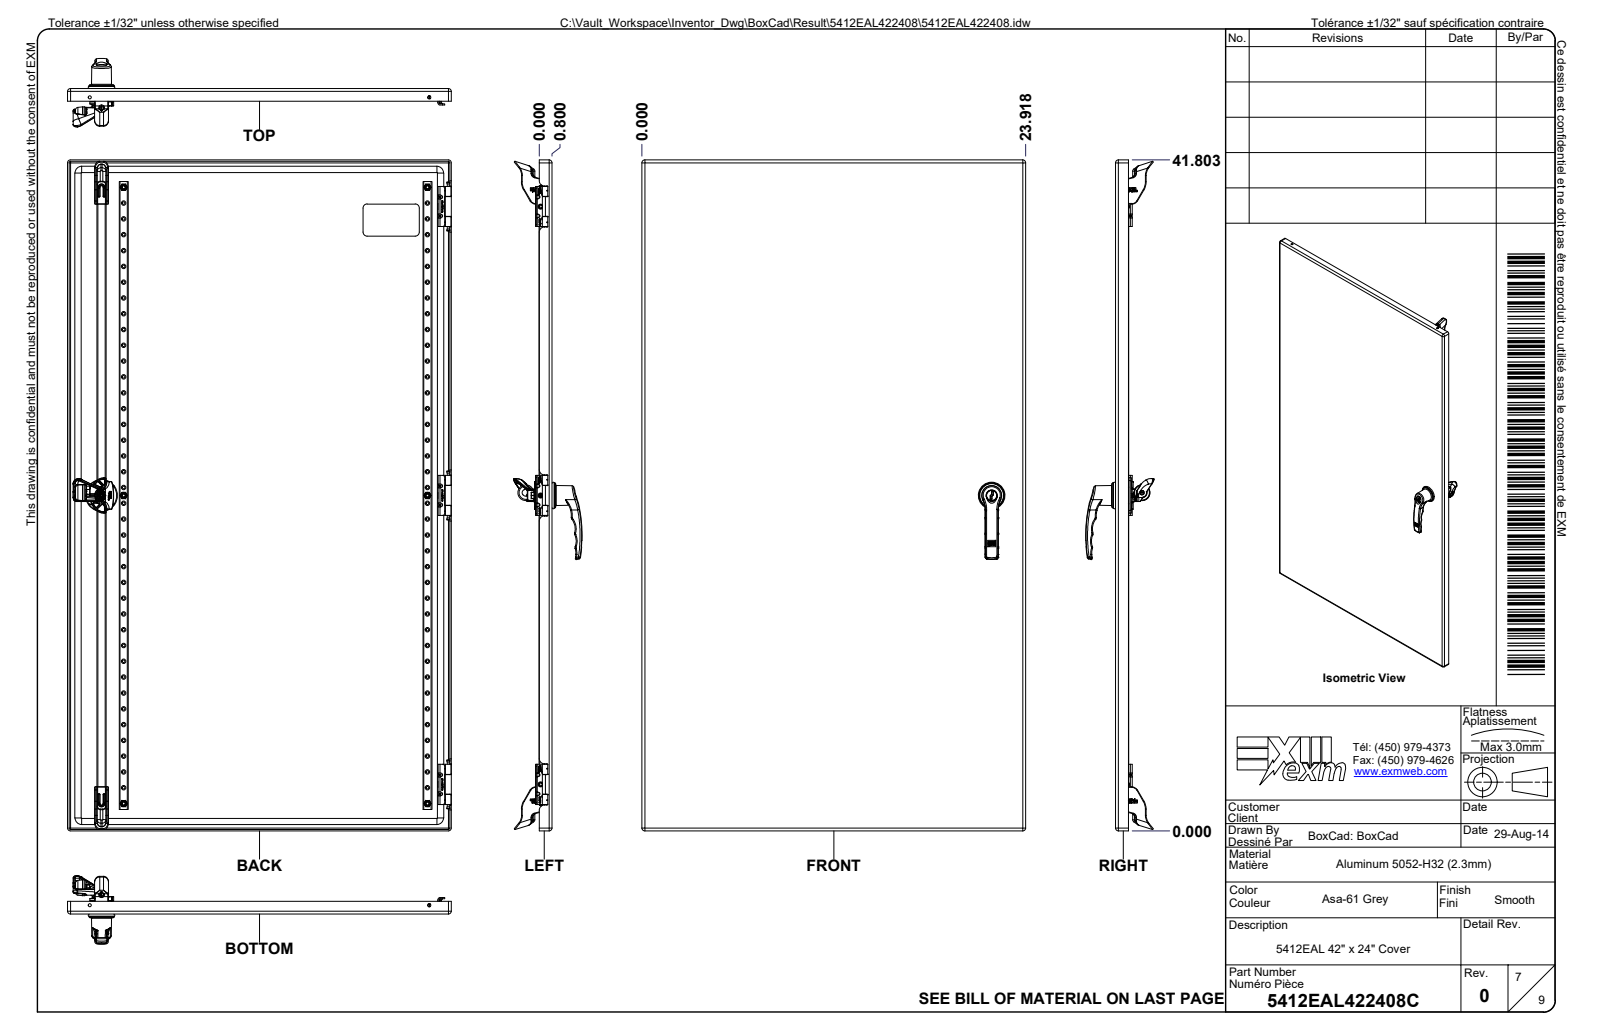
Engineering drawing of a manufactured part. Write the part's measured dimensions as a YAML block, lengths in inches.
part_name: "5412EAL422408; 5412EAL422408B; 5412EAL422408B-P; STK-Q-16010 (+8 more)"
step_written_by: "Autodesk Inventor 2024 (AUTOMOTIVE_DESIGN)"
units: inches
bodies: {solids: 90, faces: 9531, planar: 3634, cylindrical: 2085, other: 3812}
overall_size: [42, 24.042, 10.933]
volume: 427.5
surface_area: 9352
round_holes:
  - {diameter: 0.165, count: 76}
  - {diameter: 0.03, count: 15}
  - {diameter: 0.201, count: 10}
  - {diameter: 0.315, count: 10}
  - {diameter: 0.311, count: 9}
  - {diameter: 0.29, count: 7}
  - {diameter: 0.044, count: 6}
  - {diameter: 0.197, count: 6}
  - {diameter: 0.268, count: 6}
  - {diameter: 0.27, count: 6}
  - {diameter: 0.5, count: 6}
  - {diameter: 0.39, count: 4}
round_bosses_or_shafts:
  - {diameter: 0.237, count: 76}
  - {diameter: 0.03, count: 15}
  - {diameter: 0.232, count: 13}
  - {diameter: 0.039, count: 12}
  - {diameter: 0.374, count: 6}
  - {diameter: 0.311, count: 6}
  - {diameter: 0.472, count: 5}
  - {diameter: 0.717, count: 4}
partial_cylinders:
  - {radius: 0.039, count: 202}
  - {radius: 0.02, count: 191}
  - {radius: 0.01, count: 142}
  - {radius: 0.008, count: 70}
  - {radius: 0.079, count: 55}
  - {radius: 0.031, count: 38}
  - {radius: 0.059, count: 36}
  - {radius: 0.125, count: 29}
face_to_face_distances: [0.09, 8.978, 8.888, 9.068, 0.964, 0.874, 8.014, 8.104, 0.105, 1.069]
hole_center_spacings: [1.969, 0.984, 2.953, 3.937, 4.921, 5.906, 6.89, 18]
